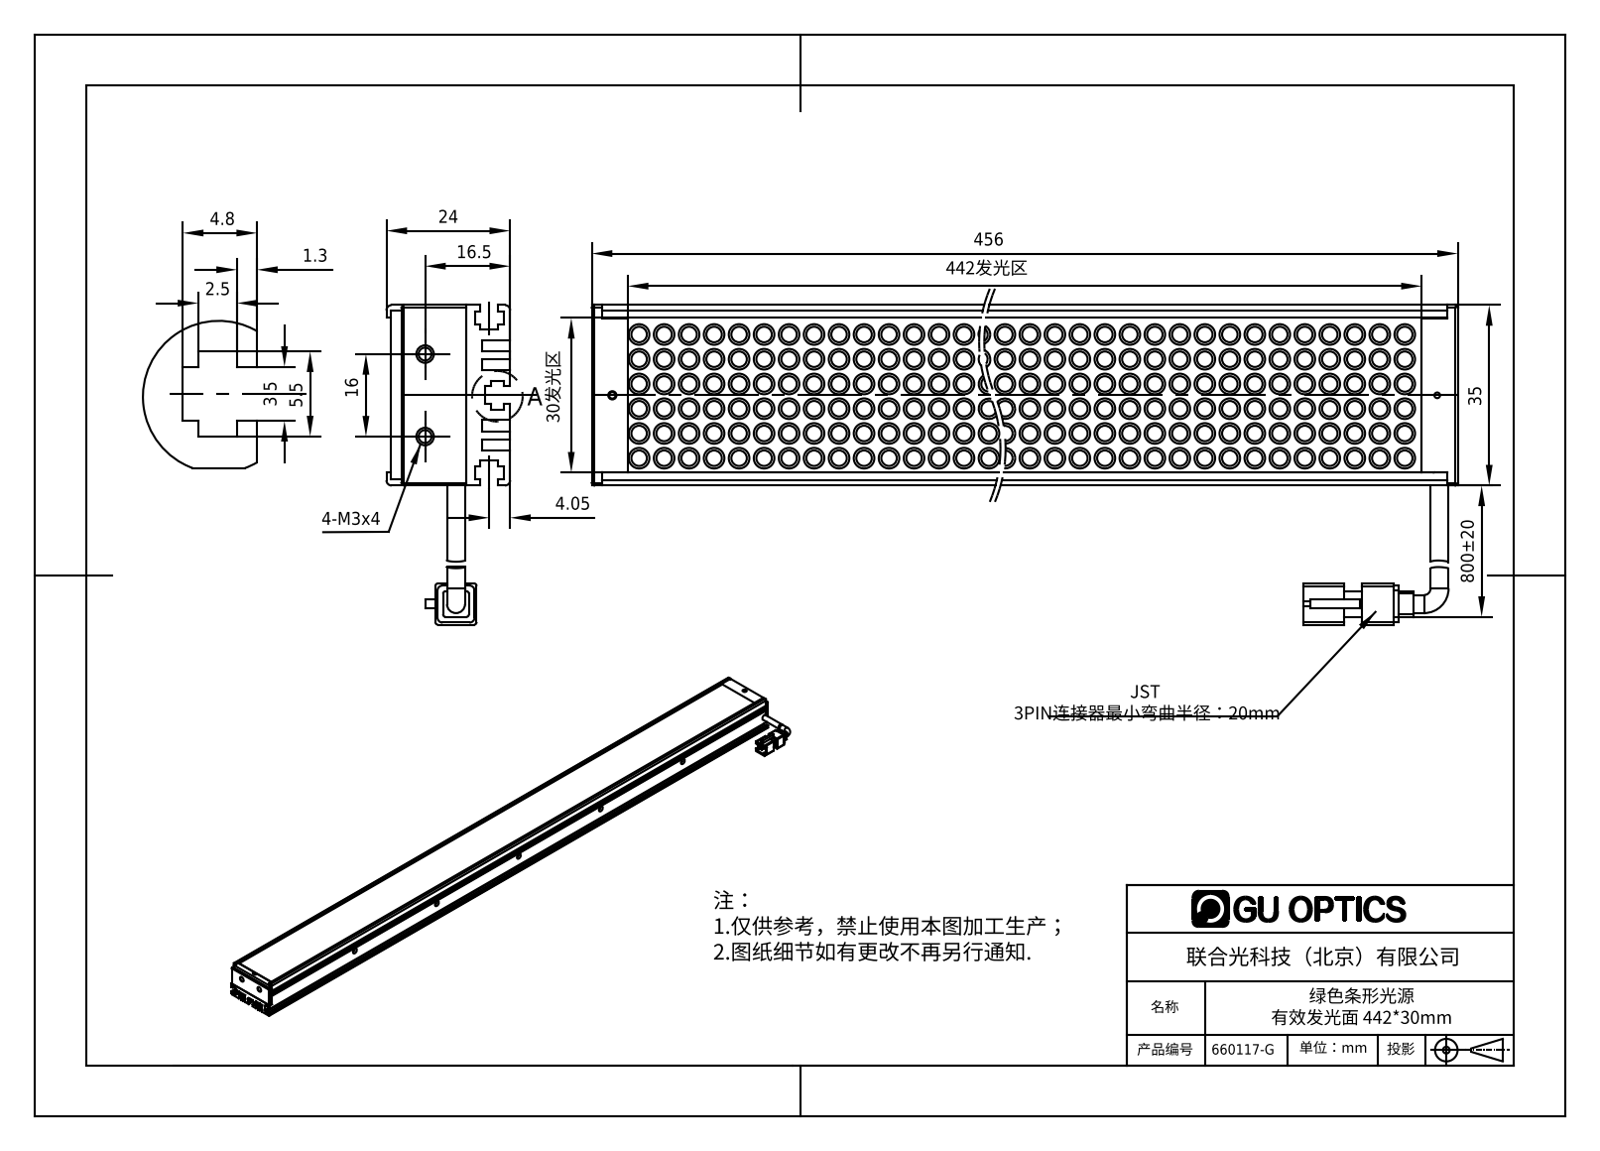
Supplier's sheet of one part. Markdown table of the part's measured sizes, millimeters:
| quantity | value |
| --- | --- |
| part name | 660117-G |
| STEP written by | SolidWorks 2016 (AUTOMOTIVE_DESIGN) |
| units | millimeters |
| bodies | 8 solids, 3753 faces (813 planar, 2279 cylindrical, 661 other) |
| overall size | 456 × 62 × 24 |
| volume | 198 847 mm³ |
| surface area | 229 218 mm² |
| round holes (diameter × count) | 1.6 × 5, 1.7 × 5, 1.5 × 2, 2.5 × 2, 2.8 × 2, 3 × 2, 1.1 × 1, 1.25 × 1, 2 × 1 |
| round bosses / shafts (diameter × count) | 4 × 546, 3 × 546, 3.5 × 2 |
| partial cylindrical surfaces (radius × count) | 1 × 12, 0.5 × 8, 1.65 × 1 |
| main face-to-face distances | 2, 2.2, 8.6, 1, 2.5, 4, 9, 10.6, 10.8, 12.6 |
| hole center spacings | 75, 150, 448, 7, 74.02, 74.2, 149.01, 149.1 |
